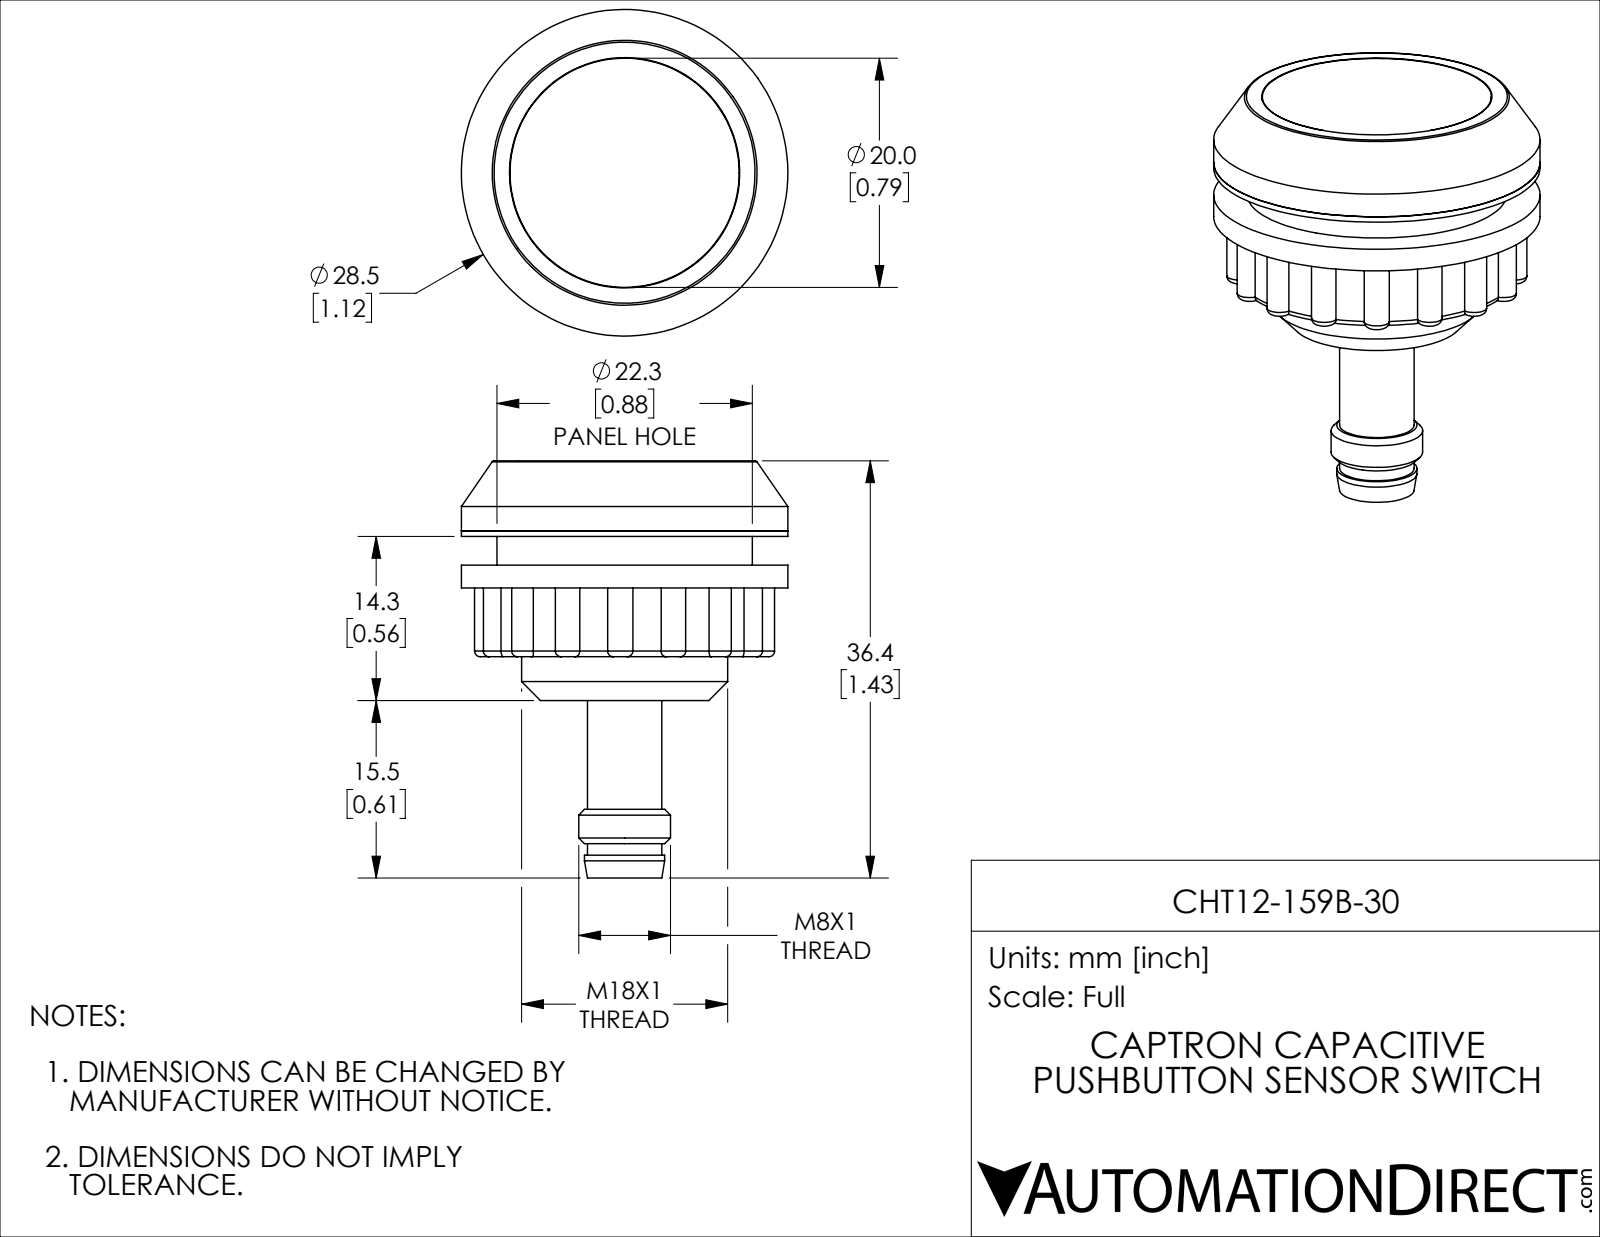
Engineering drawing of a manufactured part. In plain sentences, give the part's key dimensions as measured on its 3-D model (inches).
The part is named "CHT12-159B-30". Its 3-D file was written by "SolidWorks 2019 (CONFIG_CONTROL_DESIGN)". It is 10 solids with 192 faces: 25 planar, 91 cylindrical and 76 other. Overall it measures 1.434 by 1.122 by 1.122 inches. Its volume is 0.618 cubic inches and its surface area 11.57 square inches. Round holes: 1 of diameter 0.236, 1 of diameter 0.579, 1 of diameter 0.669, 1 of diameter 0.791, 1 of diameter 0.878, 1 of diameter 0.89. Round bosses or shafts: 5 of diameter 0.039, 1 of diameter 1.122, 1 of diameter 0.709, 1 of diameter 0.567, 1 of diameter 0.315, 1 of diameter 0.276, 1 of diameter 0.256. Partial cylindrical surfaces (rounded edges, fillets, slot ends): 16 of radius 0.043, 1 of radius 0.472. The main face-to-face distances are 0.118, 0.239, 0.259, 0.152, 0.121, 0.03, 0.088, 0.413, 0.079, 0.157.
